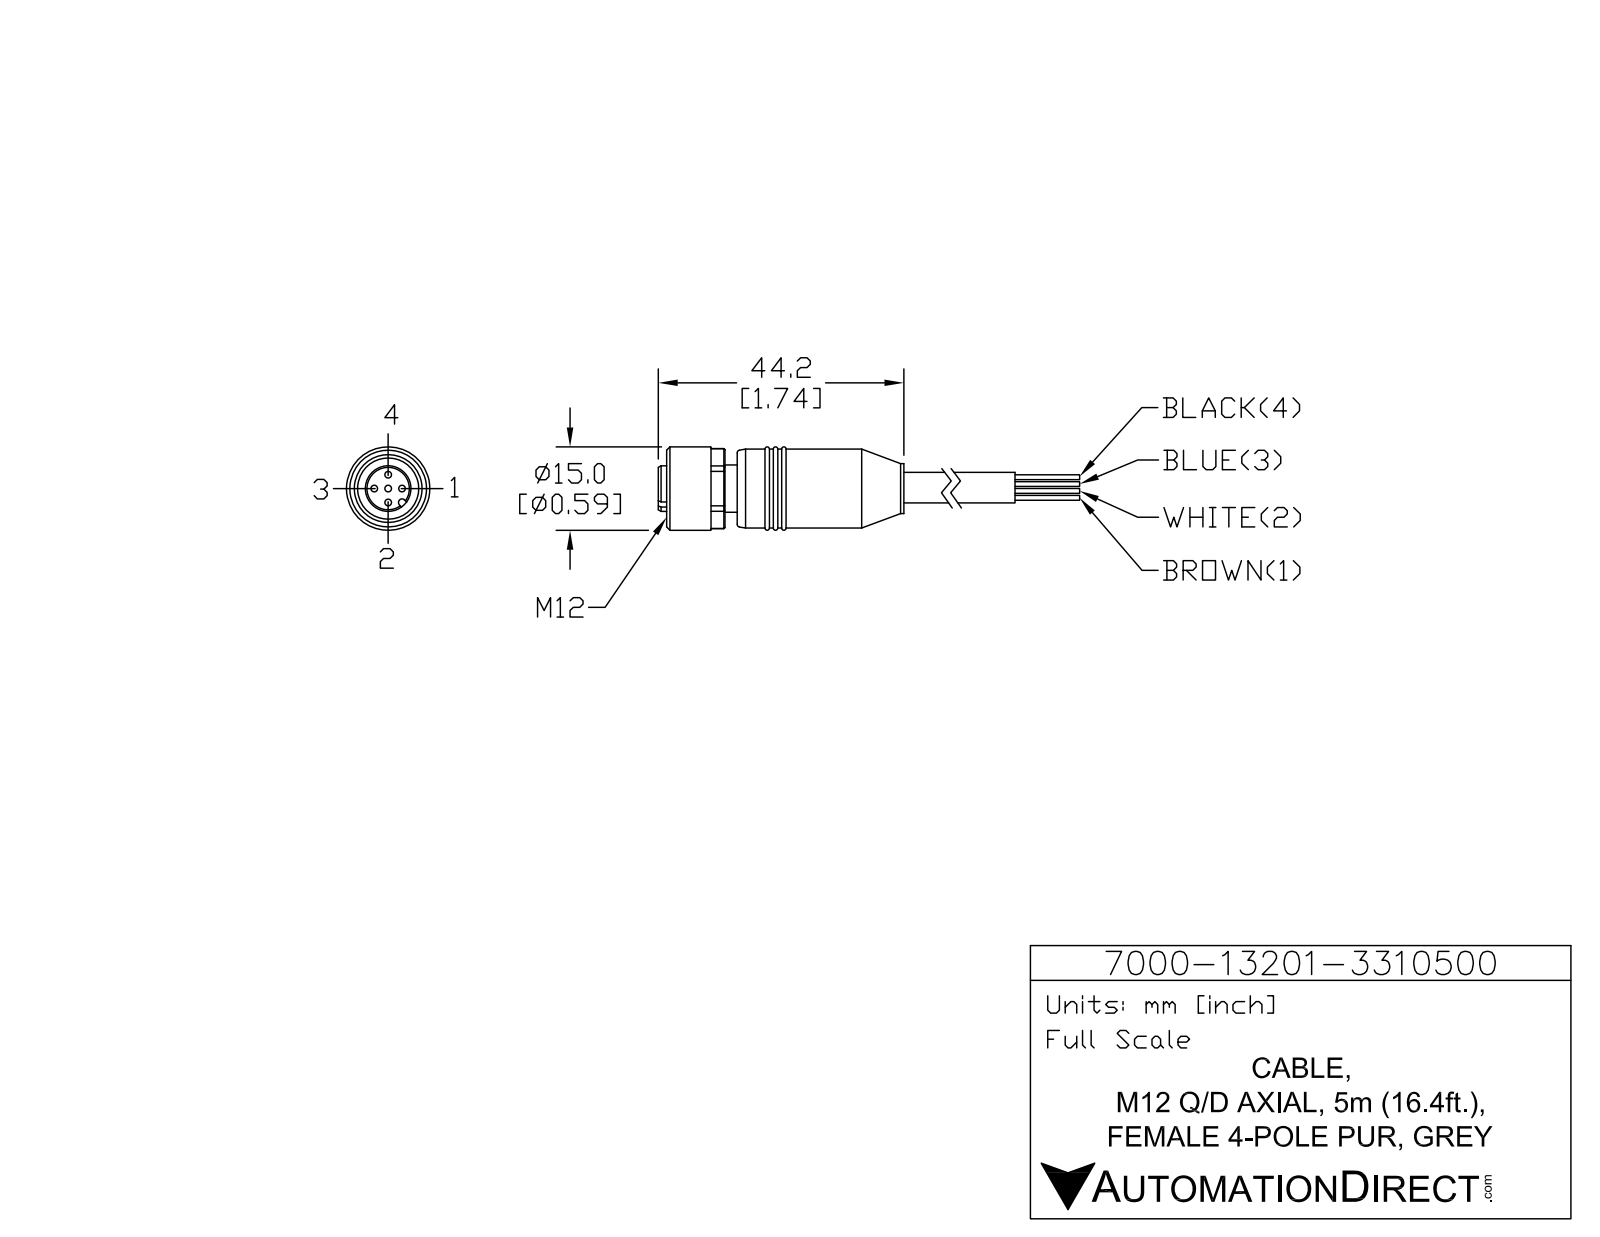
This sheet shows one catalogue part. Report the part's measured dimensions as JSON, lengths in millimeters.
{"part_name": "7000-13201-3310500", "step_written_by": "SolidWorks 2015 (AUTOMOTIVE_DESIGN)", "units": "millimeters", "bodies": {"solids": 1, "faces": 94, "planar": 28, "cylindrical": 38, "other": 28}, "overall_size": [64.2, 15, 15], "volume_mm3": 6622, "surface_area_mm2": 3349, "round_holes": [[1.2, 5], [11, 1]], "round_bosses_or_shafts": [[15, 1], [14.2, 1], [9, 1], [8.5, 1], [8.2, 1], [6.5, 1]], "partial_cylinders_radius": [[0.65, 1], [7.2, 1]], "face_to_face_distances": [2.2, 13, 3, 5.2, 9, 12, 14.2, 64.2, 55.2, 52.2], "hole_center_spacings": [2.5, 3.54, 5]}
